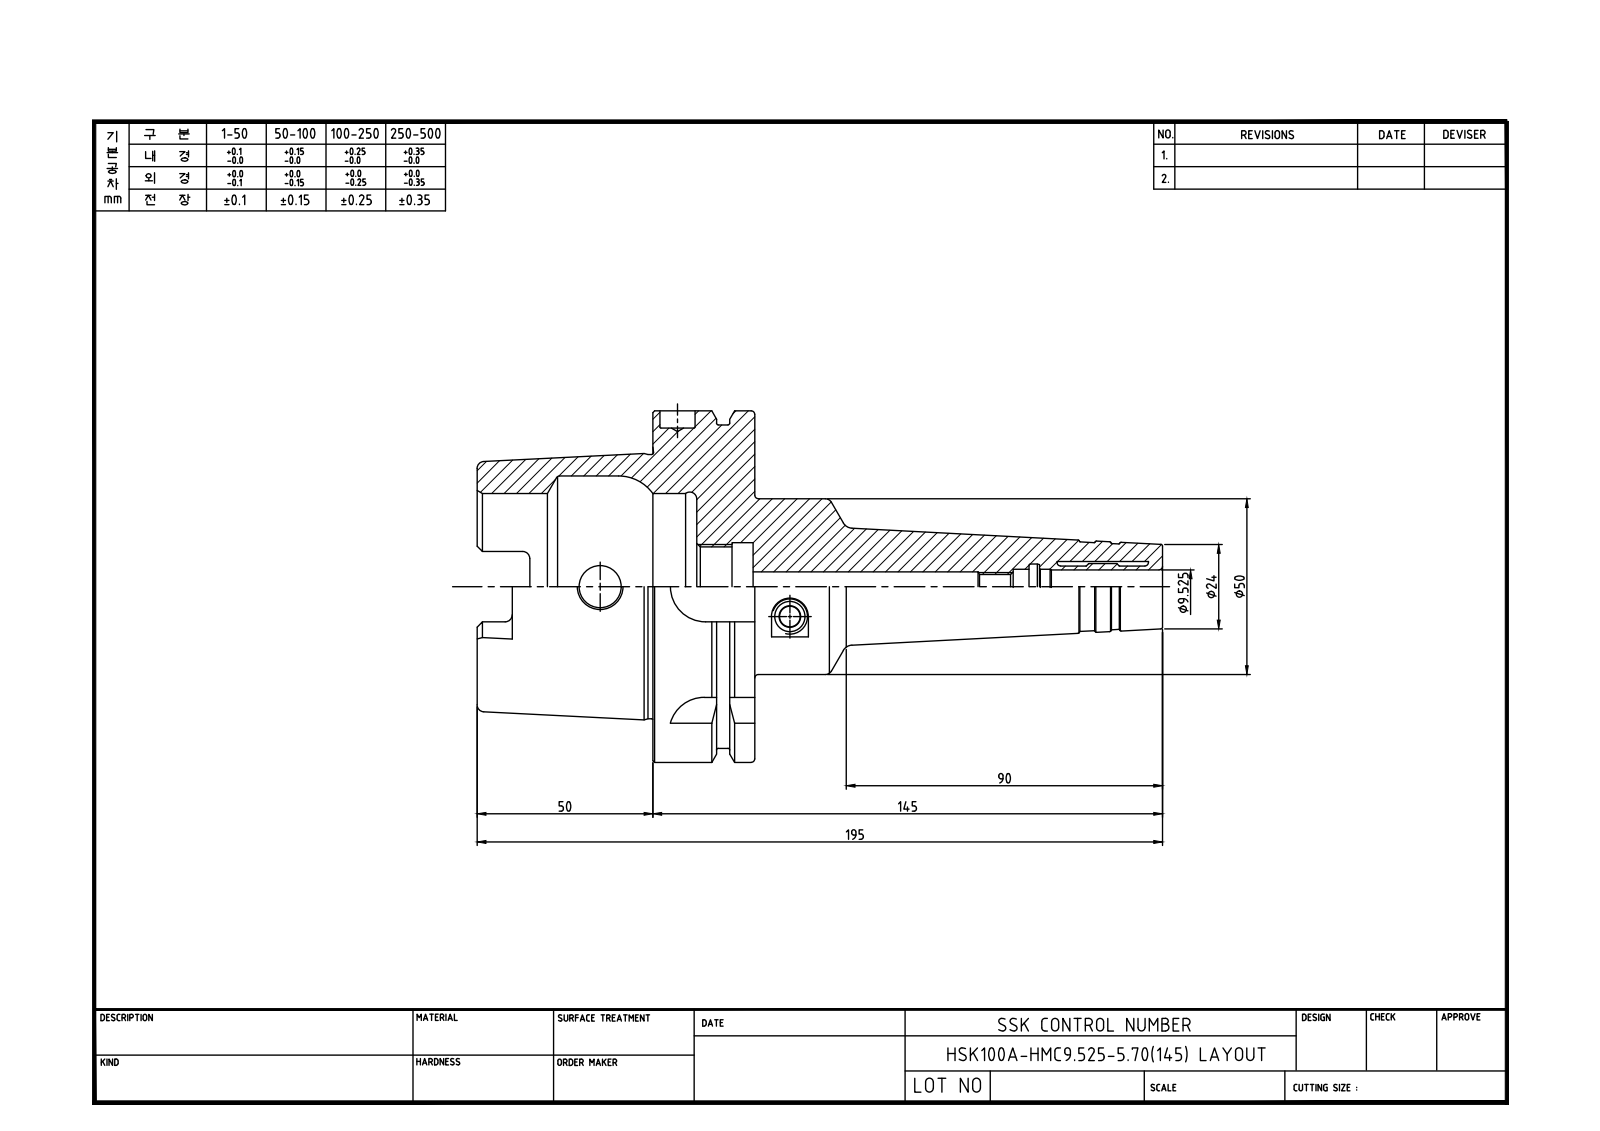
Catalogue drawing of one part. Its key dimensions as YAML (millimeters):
part_name: "HSK100A-HMC9.525-145"
step_written_by: "Autodesk Inventor 2020 (AUTOMOTIVE_DESIGN)"
units: millimeters
bodies: {solids: 1, faces: 132, planar: 38, cylindrical: 34, other: 60}
overall_size: [195, 100, 100]
volume: 355419
surface_area: 63628
round_holes:
  - {diameter: 10, count: 2}
  - {diameter: 6.92, count: 1}
  - {diameter: 9.52, count: 1}
  - {diameter: 12, count: 1}
  - {diameter: 22.38, count: 1}
  - {diameter: 25, count: 1}
  - {diameter: 53, count: 1}
  - {diameter: 63, count: 1}
round_bosses_or_shafts:
  - {diameter: 100, count: 1}
  - {diameter: 92, count: 1}
  - {diameter: 75.41, count: 1}
  - {diameter: 50, count: 1}
partial_cylinders:
  - {radius: 2, count: 6}
  - {radius: 4.88, count: 4}
  - {radius: 10, count: 4}
face_to_face_distances: [29, 12.5, 16.5, 62.5, 50, 79, 78.5, 28.5, 16, 0.5]
